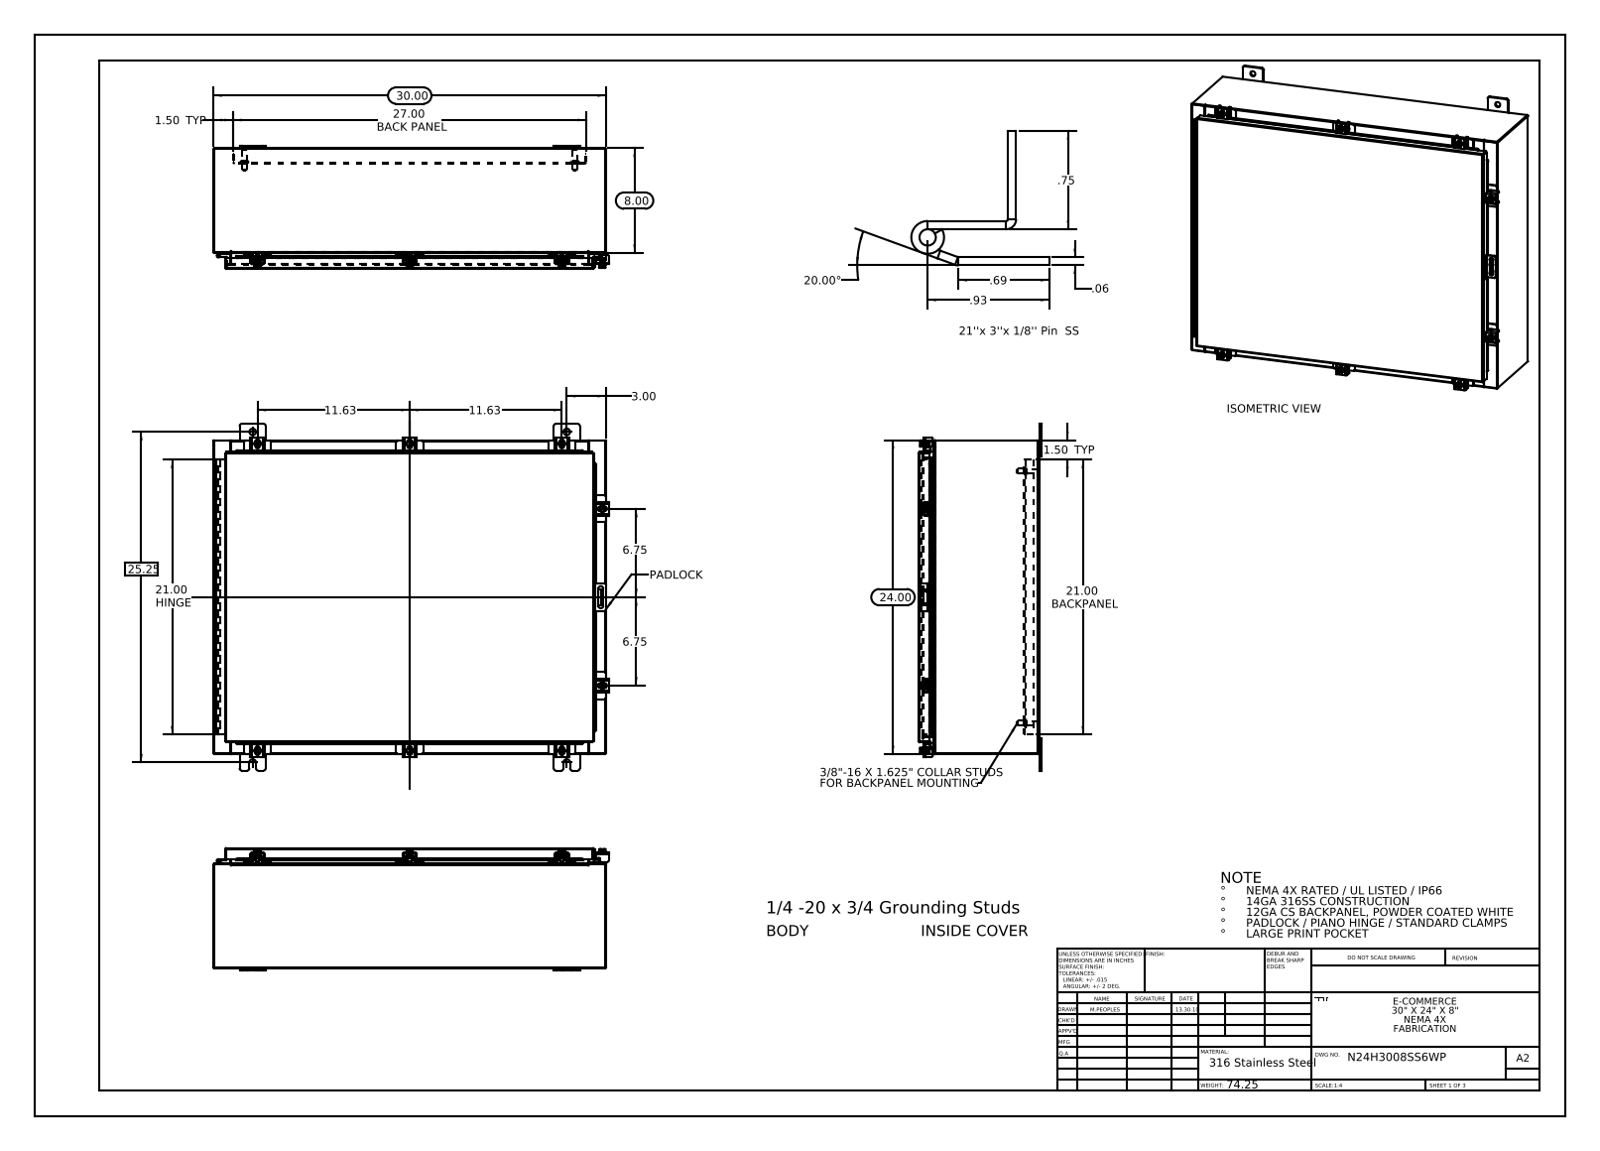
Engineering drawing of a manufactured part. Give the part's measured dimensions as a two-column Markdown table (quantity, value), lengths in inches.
| quantity | value |
| --- | --- |
| part name | N24H3008SS6WP Standard Clamps; N24H3008SS6WP Padlock Hasp; N24H3008SS6WP Hinge Enclosure Side2; N24H3008SS6WP Top (+8 more) |
| STEP written by | SolidWorks 2013 (CONFIG_CONTROL_DESIGN) |
| units | inches |
| bodies | 57 solids, 1943 faces (1028 planar, 803 cylindrical, 112 other) |
| overall size | 30.211 × 26.5 × 9.389 |
| volume | 260.9 in³ |
| surface area | 6 534 in² |
| round holes (diameter × count) | 0.213 × 8, 0.26 × 8, 0.5 × 8, 0.125 × 2, 0.125 × 1 |
| round bosses / shafts (diameter × count) | 0.25 × 9, 0.5 × 8, 0.399 × 8, 0.625 × 4, 0.375 × 4, 0.33 × 4 |
| partial cylindrical surfaces (radius × count) | 0.06 × 38, 0.013 × 25, 0.19 × 24, 0.088 × 21, 0.12 × 16, 0.141 × 16, 0.05 × 11, 0.08 × 10 |
| main face-to-face distances | 0.075, 9.126, 9.201, 9.051, 0.104, 1, 1.075, 8.051, 8.126, 1.179 |
| hole center spacings | 21.374, 24, 26.174, 23.451, 1.858, 2.326, 2.326, 3.065 |
